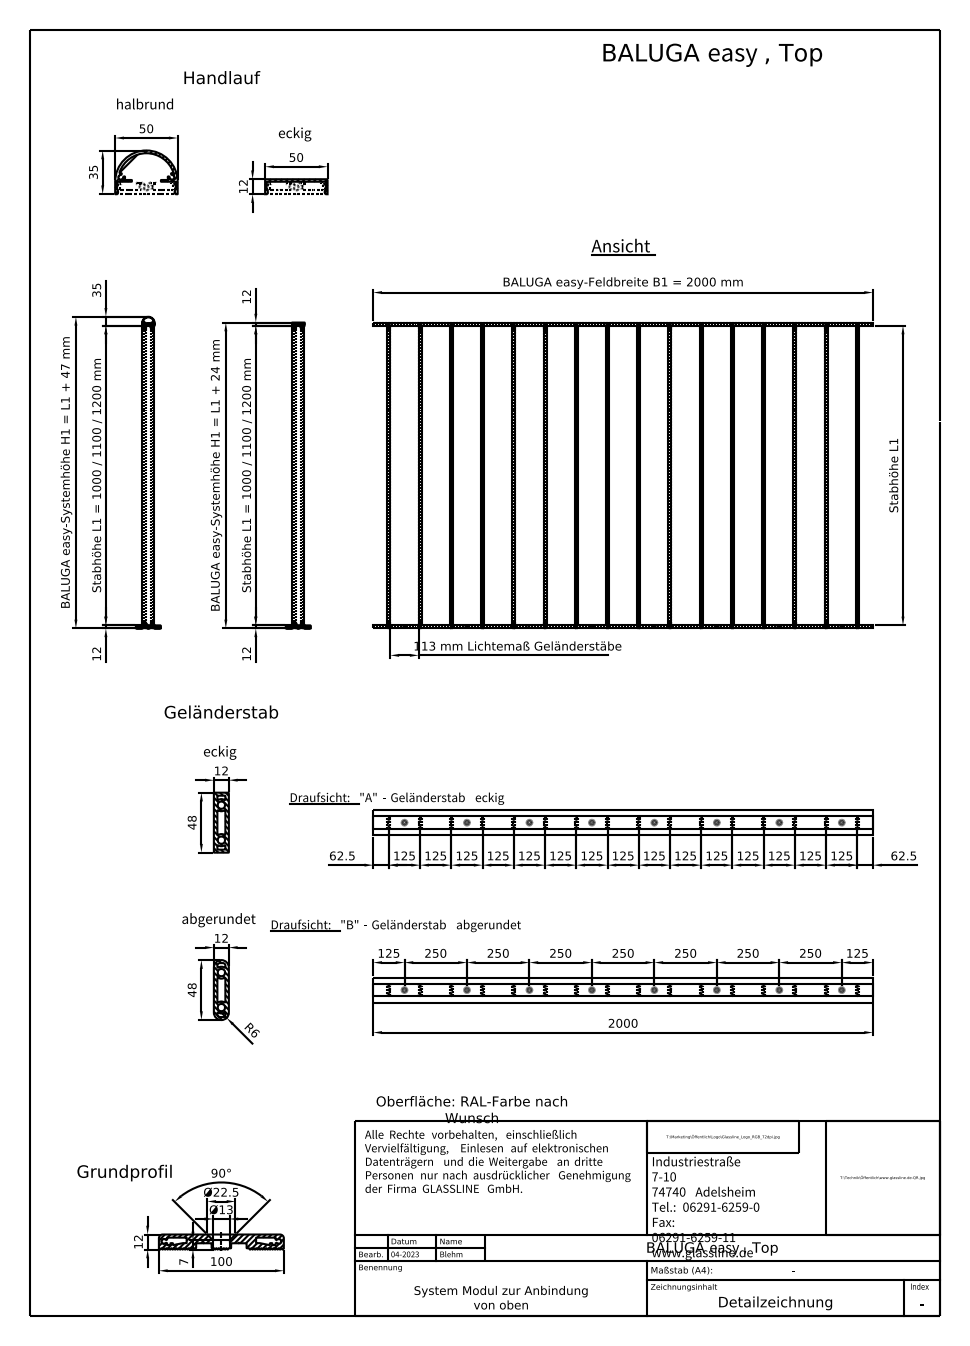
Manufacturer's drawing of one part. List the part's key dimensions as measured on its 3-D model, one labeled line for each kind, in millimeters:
Part name (STEP PRODUCT): Top Varianten; Top Profil 2000mm; Geländerstab rechteckig 1200mm; Geländerstab abgerundet 1200mm (+3 more)
STEP written by: Autodesk Inventor 2023 (AUTOMOTIVE_DESIGN)
Units: millimetres
Bodies: 76 solids, 7388 faces (3460 planar, 3896 cylindrical, 32 other)
Overall size (bounding box): 3100 × 2000 × 1247.02
Volume: 36 570 000 mm³ · Surface area: 24 500 000 mm²
Round holes (diameter × count): ⌀6.5 ×192, ⌀13 ×32
Partial cylindrical surfaces — rounded edges, fillets, slot ends (radius × count): R0.5 ×972, R0.2 ×276, R0.3 ×276, R2 ×152, R3 ×136, R2.9 ×128, R4.85 ×128, R4.7 ×64
Main face-to-face distances: 125, 250, 375, 500, 12, 625, 137, 113, 1000, 262
Hole centre spacings: 250, 64.05, 125, 128.11, 188.02, 312.81, 500, 251.57
